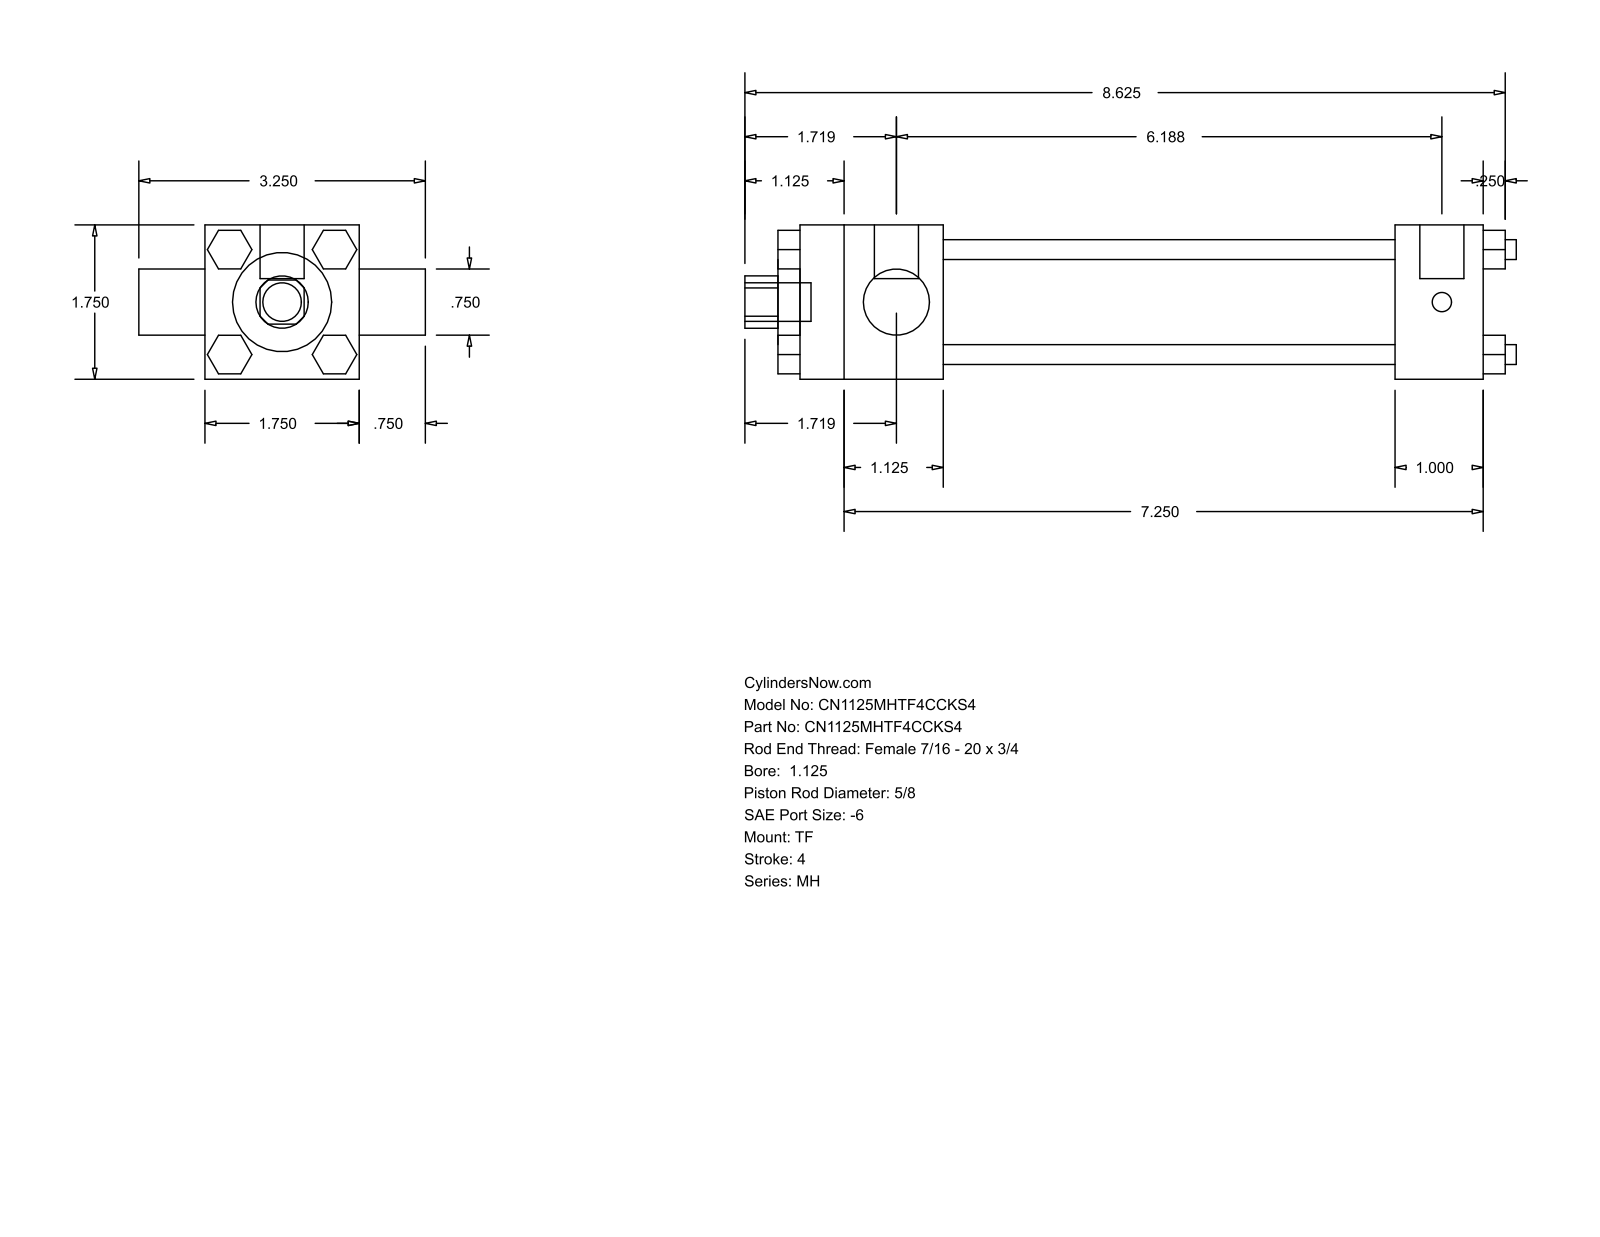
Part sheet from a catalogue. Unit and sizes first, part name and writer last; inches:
Units: inches
Overall size (bounding box): 8.75 × 3.25 × 1.75
Round holes (diameter × count): ⌀0.625 ×1, ⌀0.75 ×1, ⌀1.125 ×1, ⌀1.375 ×1
Round bosses / shafts (diameter × count): ⌀0.225 ×4, ⌀0.219 ×3, ⌀0.5 ×2, ⌀0.437 ×1
Partial cylindrical surfaces — rounded edges, fillets, slot ends (radius × count): R0.297 ×1
Main face-to-face distances: 1.75, 0.25, 8, 0.437, 5.125, 6.125, 1, 1.625, 6.75, 7.75
Bodies: 0 solids, 120 faces (92 planar, 28 cylindrical, 0 other)
Part name (STEP PRODUCT): MH_TF__0112_0.625
STEP written by: GSSL Pune (CONFIG_CONTROL_DESIGN)
